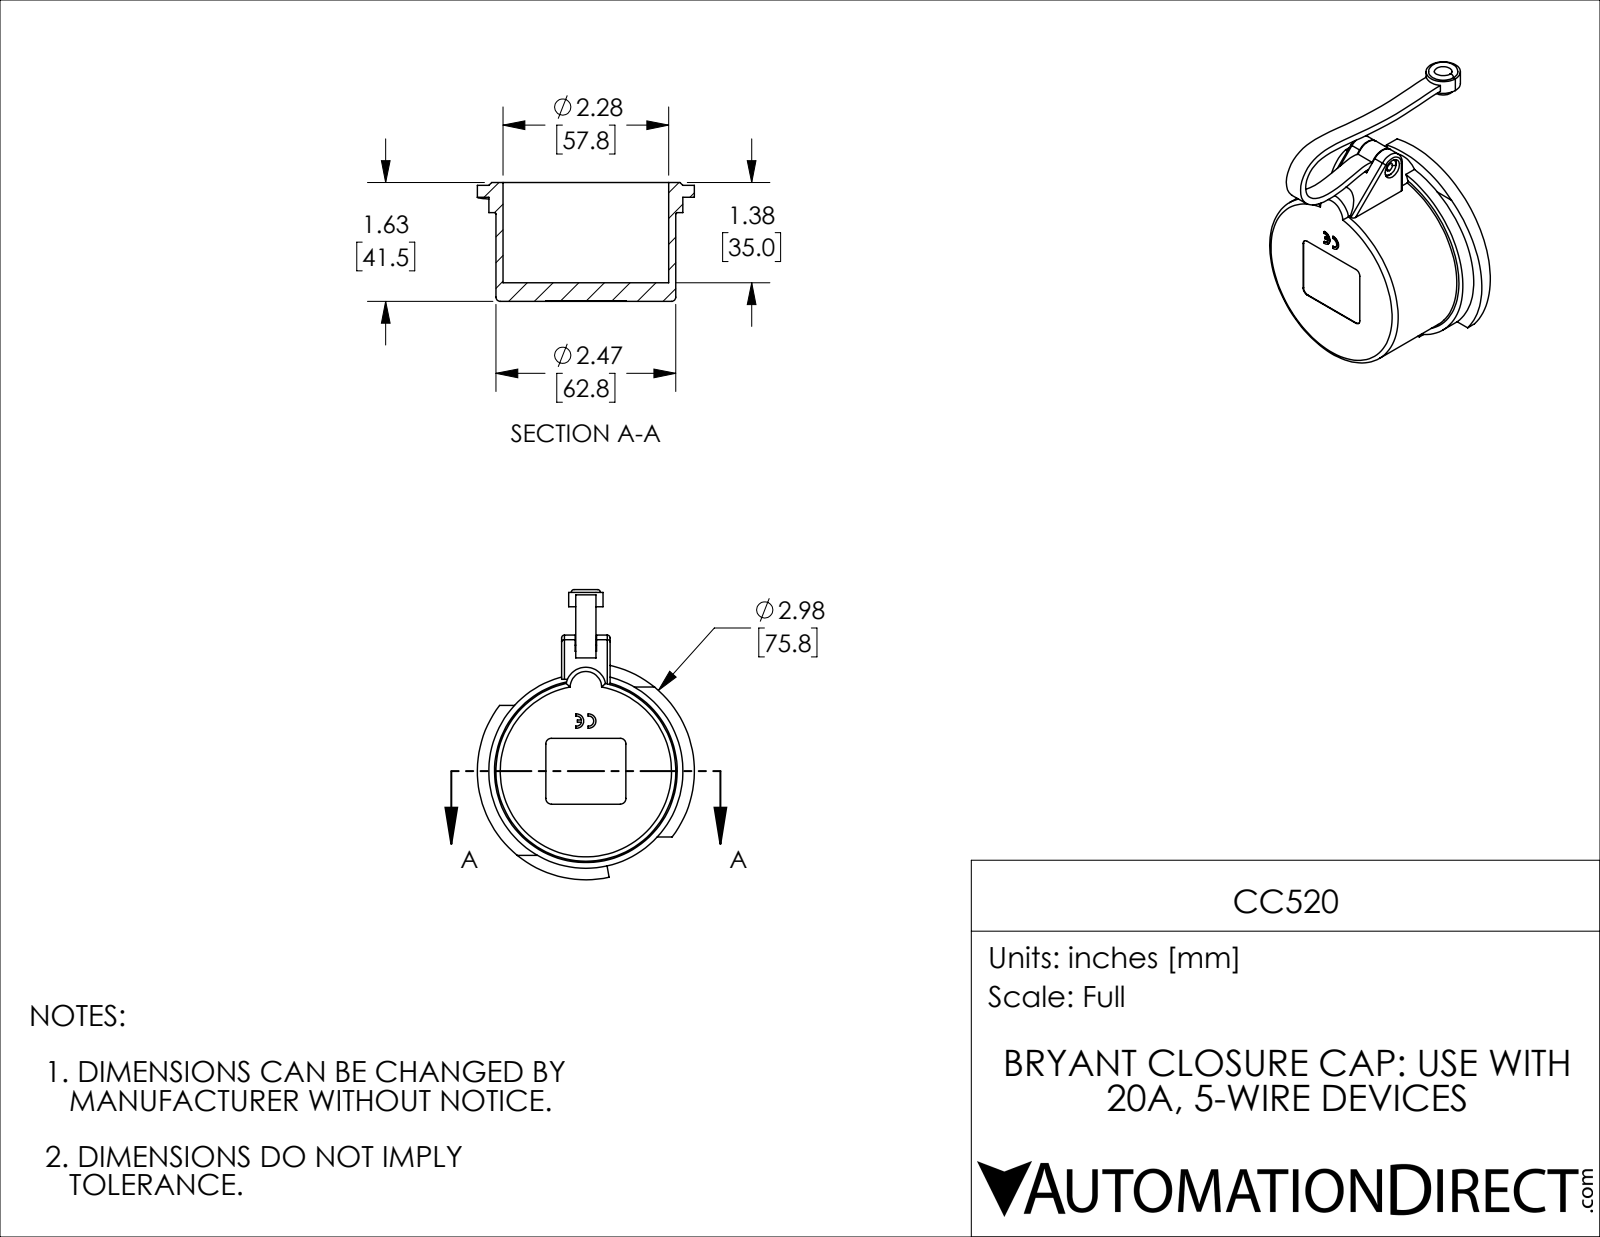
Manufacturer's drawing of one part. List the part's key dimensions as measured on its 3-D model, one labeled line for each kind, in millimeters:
Part name (STEP PRODUCT): CC520
STEP written by: SolidWorks 2021 (CONFIG_CONTROL_DESIGN)
Units: millimetres
Bodies: 1 solid, 133 faces (49 planar, 63 cylindrical, 21 other)
Overall size (bounding box): 101.3 × 80 × 75.8
Volume: 51 030 mm³ · Surface area: 28 120 mm²
Round holes (diameter × count): ⌀3 ×1, ⌀4.3 ×1, ⌀5 ×1, ⌀6.2 ×1, ⌀7 ×1, ⌀57.8 ×1
Round bosses / shafts (diameter × count): ⌀67.8 ×1, ⌀62.8 ×1, ⌀12 ×1, ⌀11 ×1, ⌀7 ×1, ⌀6 ×1, ⌀4 ×1
Partial cylindrical surfaces — rounded edges, fillets, slot ends (radius × count): R1 ×4, R2 ×4, R1.8 ×2, R2.5 ×2, R3.5 ×1, R7 ×1, R37.9 ×1
Main face-to-face distances: 6.5, 41.5, 35, 40.5, 34, 1, 6.3, 40.3, 41.3, 10.5
